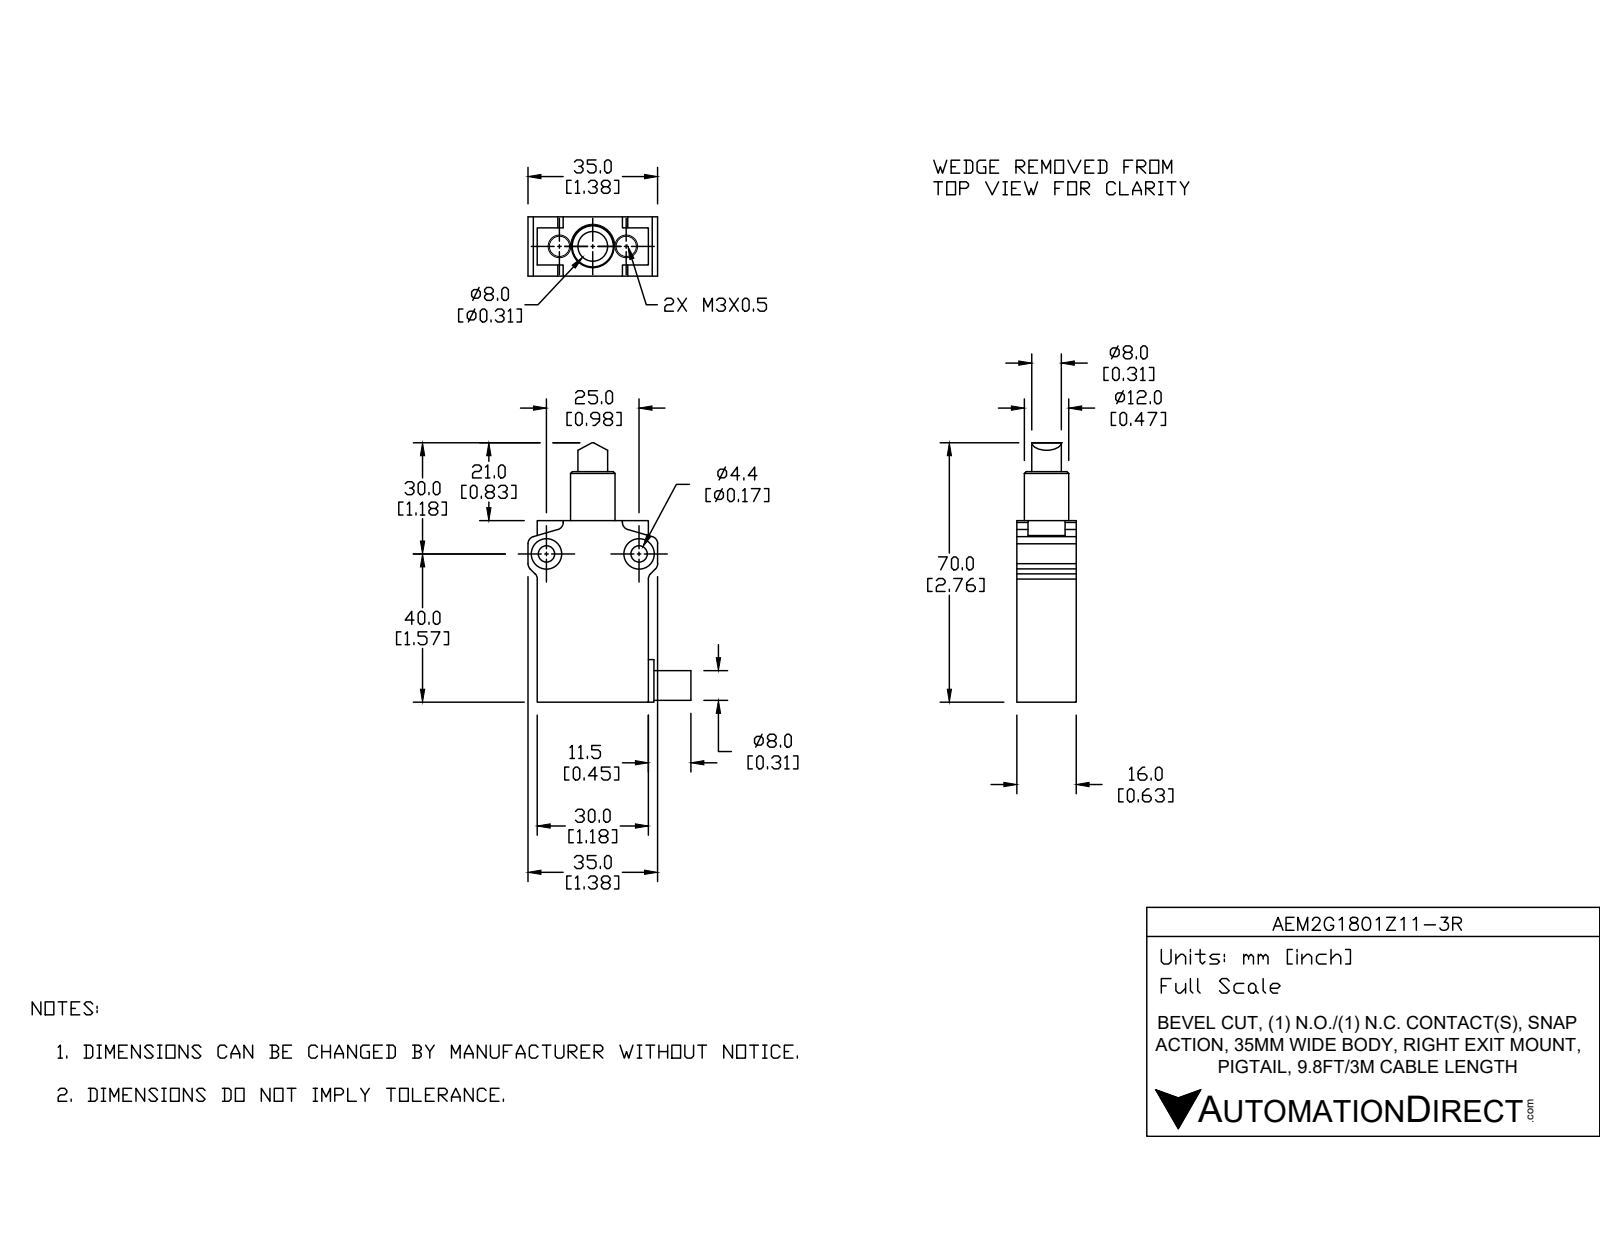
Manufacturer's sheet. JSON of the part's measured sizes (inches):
{"part_name": "AEM2G1801Z11-3R", "step_written_by": "SolidWorks 2017 (AUTOMOTIVE_DESIGN)", "units": "inches", "bodies": {"solids": 4, "faces": 101, "planar": 49, "cylindrical": 45, "other": 7}, "overall_size": [2.756, 1.87, 0.63], "volume_in3": 1.539, "surface_area_in2": 13.75, "round_holes": [[0.118, 2], [0.173, 2], [0.323, 2], [0.317, 1]], "round_bosses_or_shafts": [[0.472, 1], [0.323, 1], [0.315, 1]], "partial_cylinders_radius": [[0.079, 8], [0.03, 1], [0.256, 1]], "face_to_face_distances": [0.63, 1.181, 0.472, 1.929, 1.74, 0.189, 0.098, 1.28, 0.157, 0.039], "hole_center_spacings": [0.374, 0.748, 0.984]}
